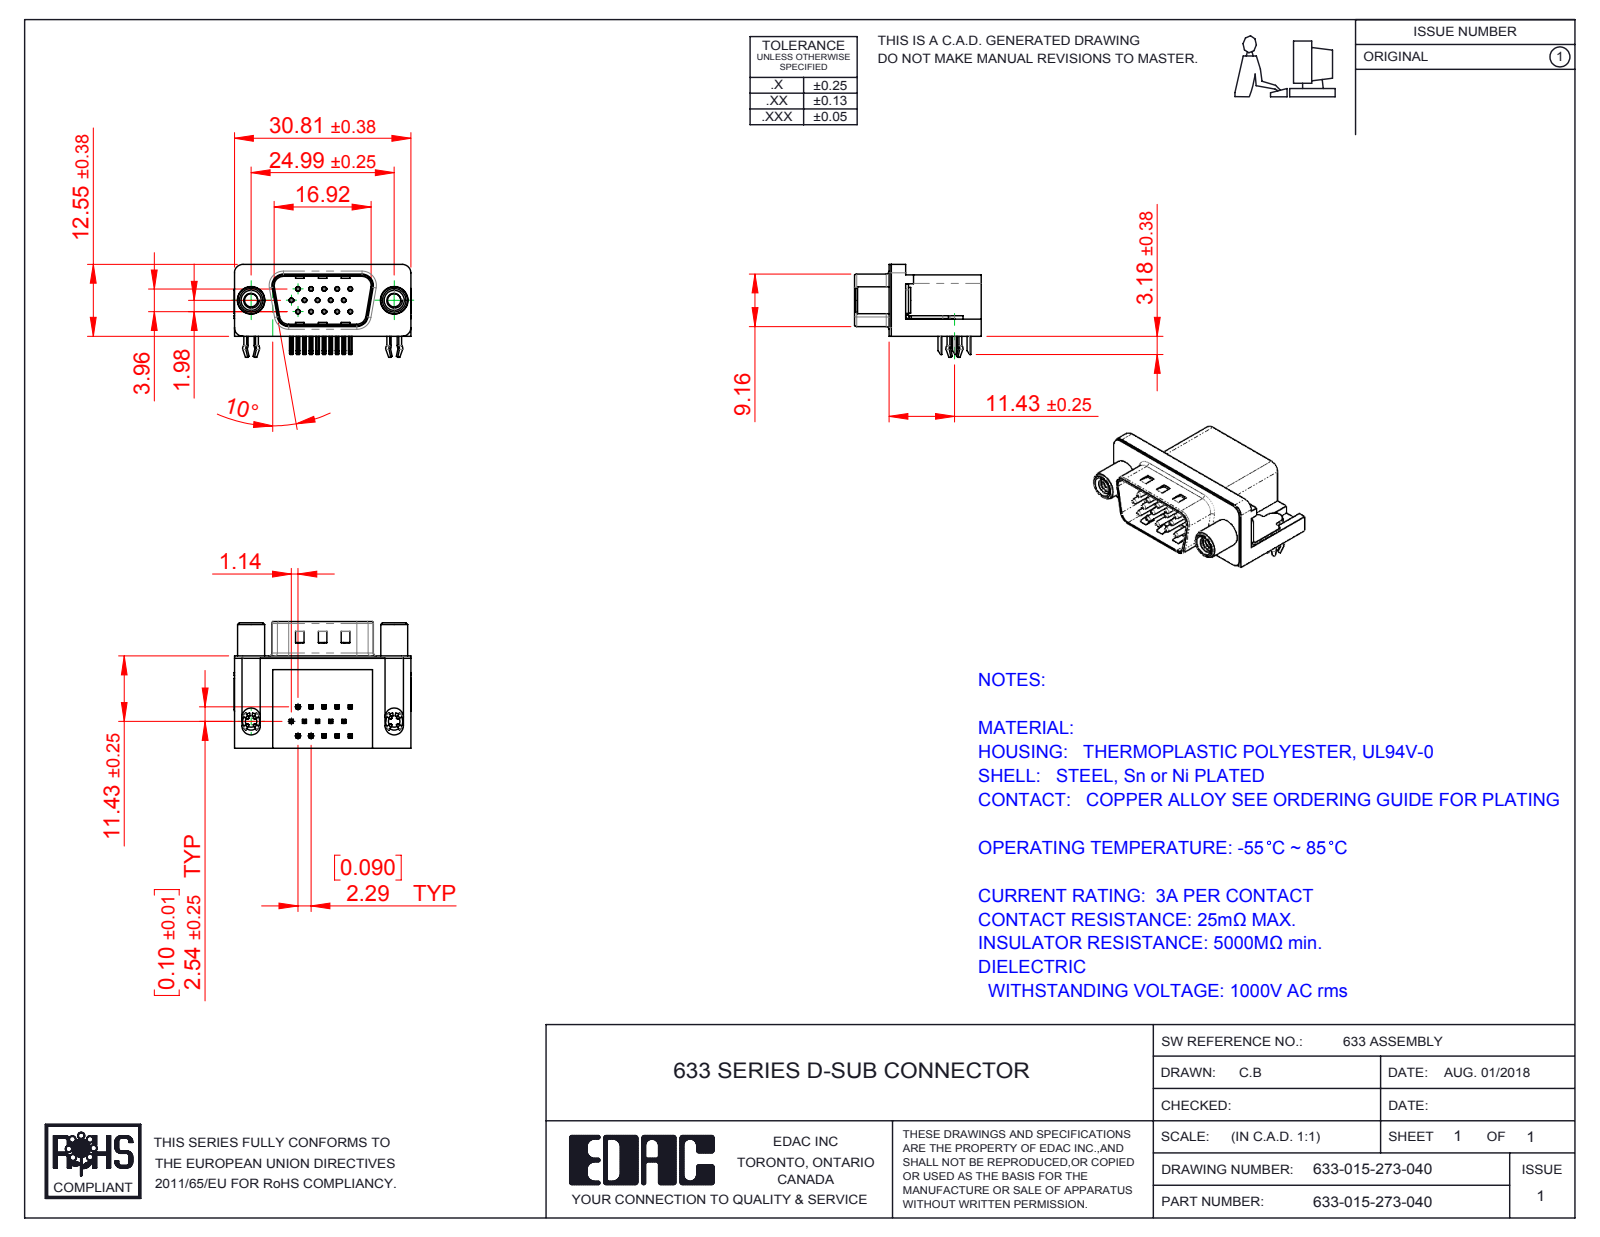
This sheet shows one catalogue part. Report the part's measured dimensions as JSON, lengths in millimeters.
{"part_name": "633 Contact Top; 633 Contact Middle; 633 Round Threaded Standoff; 633 Shell_15 Contact (+5 more)", "step_written_by": "SolidWorks 2016 (CONFIG_CONTROL_DESIGN)", "units": "millimeters", "bodies": {"solids": 21, "faces": 1557, "planar": 895, "cylindrical": 457, "other": 205}, "overall_size": [30.89, 22.1, 16.25], "volume_mm3": 4173, "surface_area_mm2": 5695, "round_holes": [[0.35, 15], [0.8, 15], [2, 2], [2.3, 2], [3.1, 2], [4, 2], [4.8, 2], [5, 2]], "round_bosses_or_shafts": [[0.75, 15], [4.9, 2], [4.7, 2], [4.5, 2], [3.85, 2], [3, 2]], "partial_cylinders_radius": [[0.25, 64], [0.12, 30], [1, 16], [0.5, 9], [1.6, 8], [1.5, 7], [0.9, 4], [2, 4]], "face_to_face_distances": [0.4, 10.35, 15.7, 2.9, 6.7, 2.5, 16.1, 0.35, 10.7, 13.2], "hole_center_spacings": [3.96, 2.28, 4.57, 2.29, 6.05, 6.86, 7.92, 6.04]}
